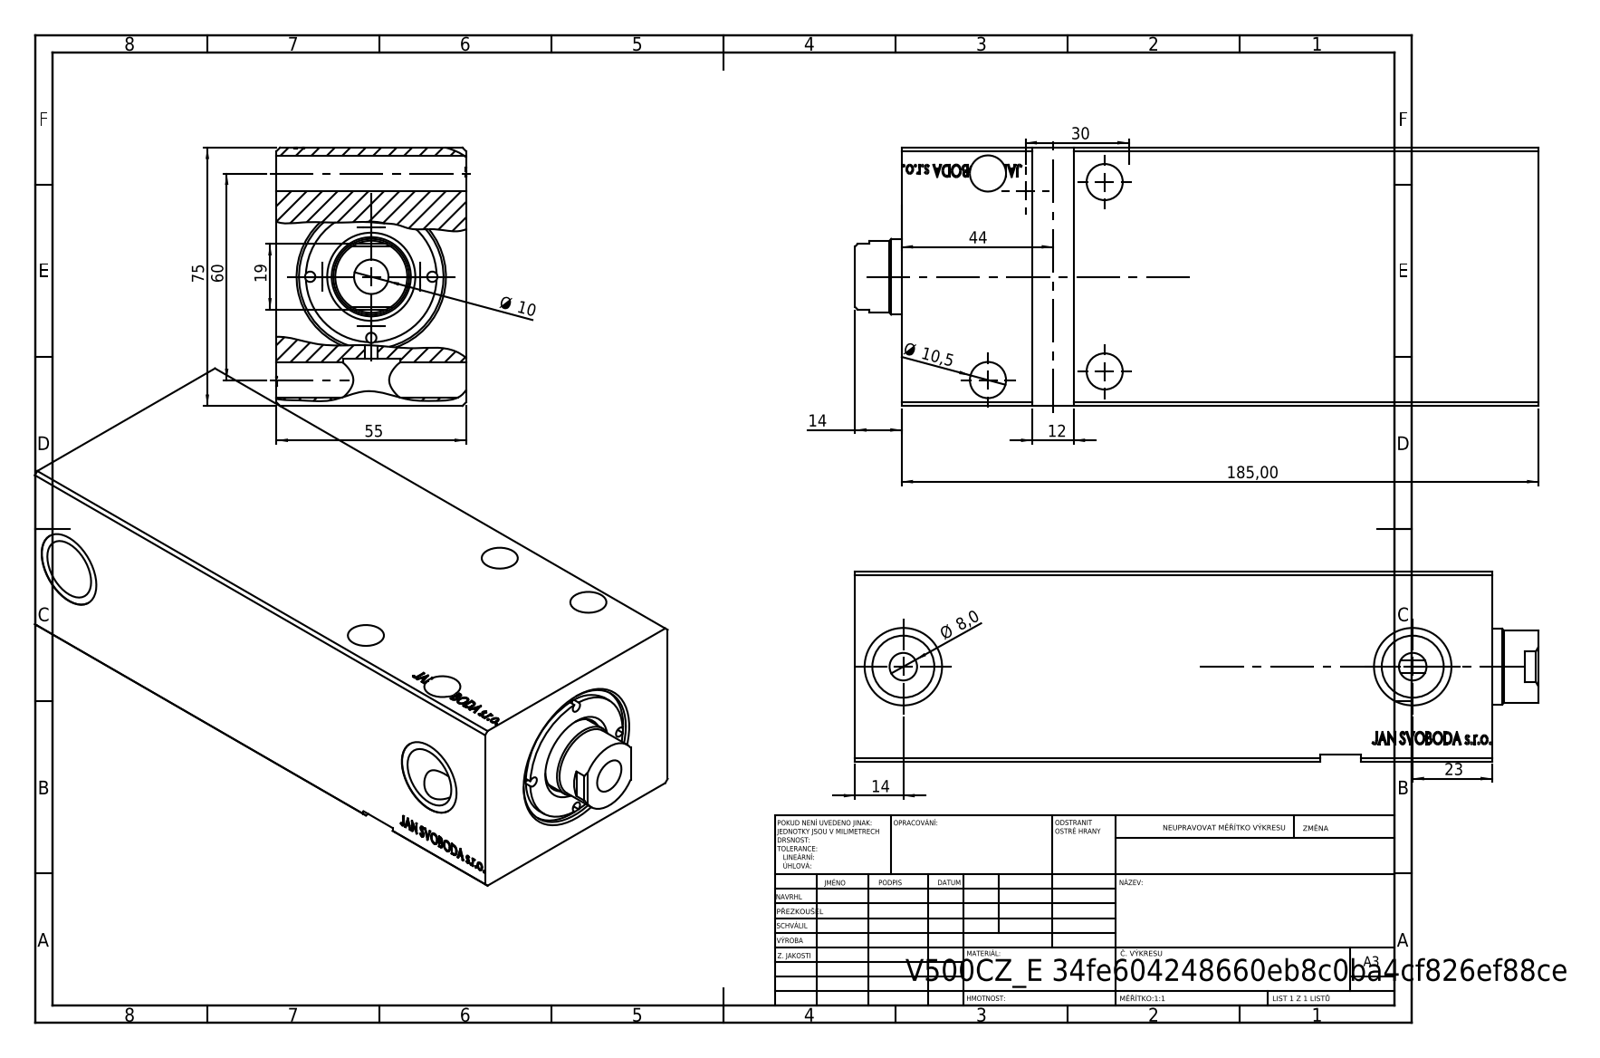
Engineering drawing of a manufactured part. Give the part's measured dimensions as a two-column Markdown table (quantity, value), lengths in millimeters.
| quantity | value |
| --- | --- |
| part name | V500CZ_VCP_E; V500CZ_VC_vysunovaci_E; V500CZ_E |
| STEP written by | SolidWorks 2019 (CONFIG_CONTROL_DESIGN) |
| units | millimeters |
| bodies | 3 solids, 782 faces (376 planar, 54 cylindrical, 352 other) |
| overall size | 198.5 × 75 × 55 |
| volume | 688 601 mm³ |
| surface area | 98 952 mm² |
| round holes (diameter × count) | 3 × 4, 10.5 × 4, 8 × 2, 18 × 2, 22.5 × 2, 10 × 1, 22 × 1, 23 × 1, 32 × 1, 36 × 1, 42 × 1 |
| round bosses / shafts (diameter × count) | 38 × 1, 20.92 × 1 |
| main face-to-face distances | 55, 75, 185, 155, 30, 184.8, 29.8, 11.8, 143.2, 173 |
| hole center spacings | 17.75, 25.1, 34, 35.5, 66.75, 55, 60, 148 |
